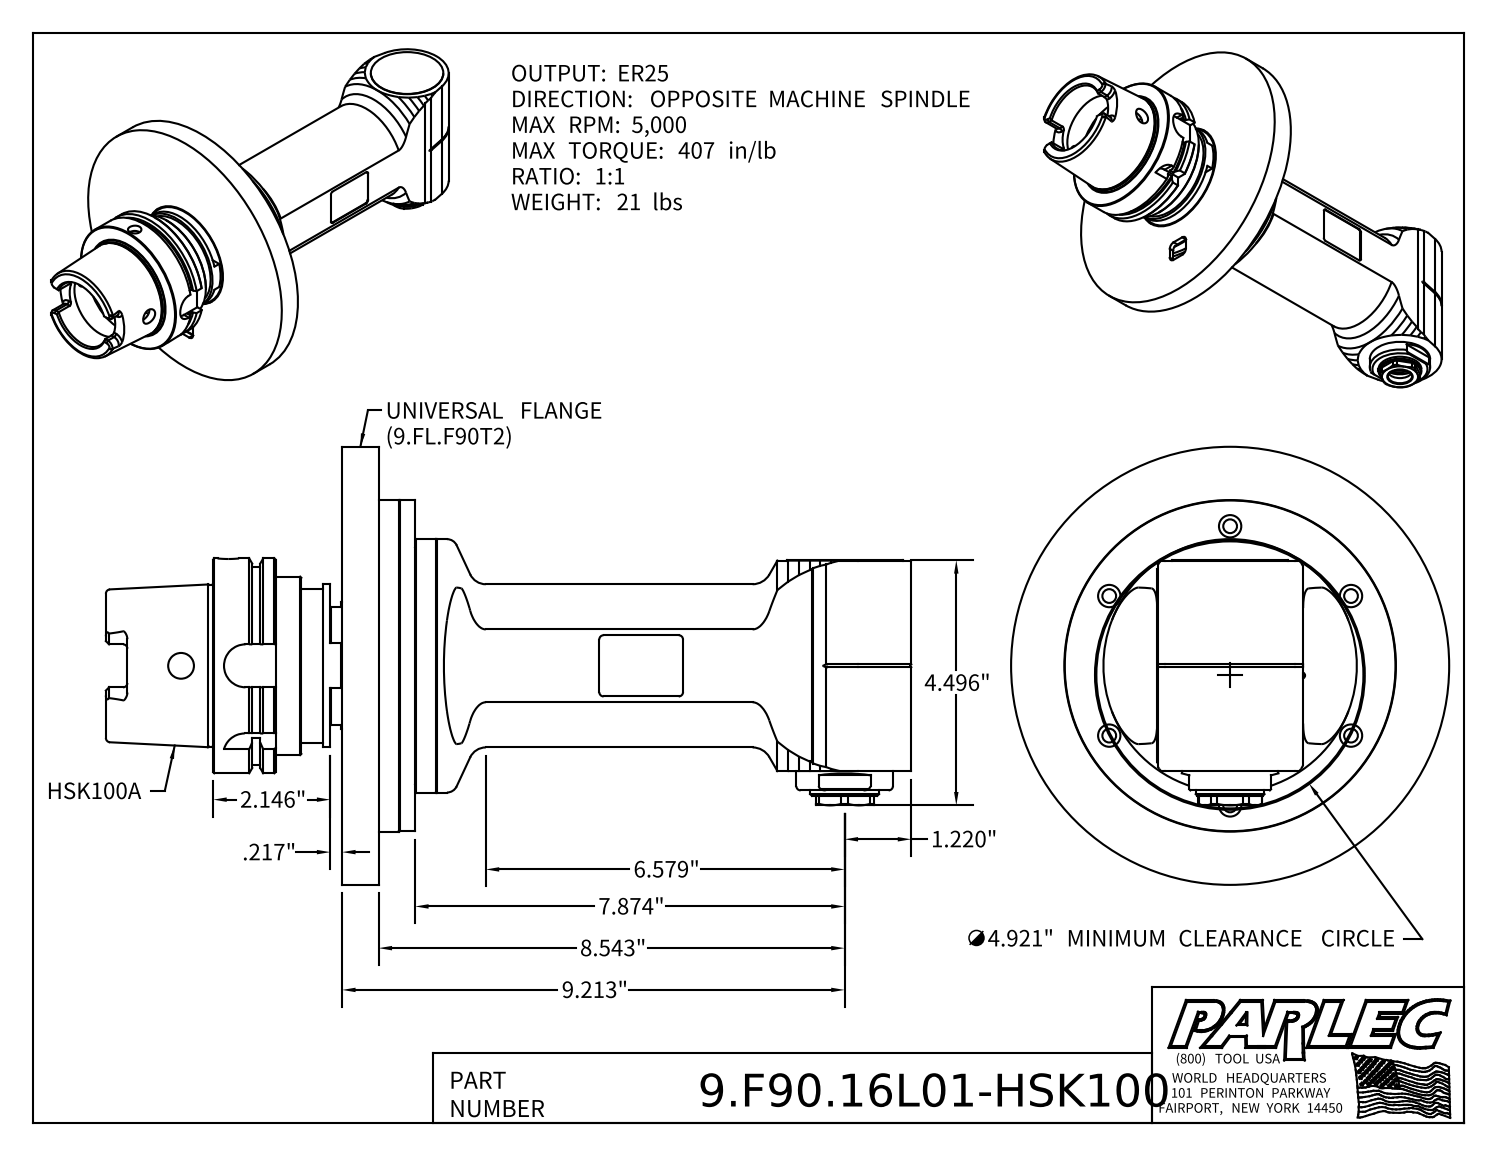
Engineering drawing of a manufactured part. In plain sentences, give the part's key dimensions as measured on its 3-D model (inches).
The part is named "9.F90.16L01-HSK100; 9_SK_51_2 (EVO, HSK100, MTC); 9_F90_16L01". Its 3-D file was written by "Autodesk Inventor 2022 (AUTOMOTIVE_DESIGN)". It is 4 solids with 429 faces: 186 planar, 121 cylindrical and 122 other. Overall it measures 14.764 by 8.031 by 8.031 inches. Its volume is 148 cubic inches and its surface area 448.8 square inches. Round holes: 10 of diameter 0.409, 6 of diameter 0.252, 1 of diameter 0.394, 1 of diameter 0.472, 1 of diameter 0.492, 1 of diameter 0.709, 1 of diameter 0.787, 1 of diameter 1.008, 1 of diameter 1.102, 1 of diameter 1.201, 1 of diameter 1.28, 1 of diameter 2.087. Round bosses or shafts: 4 of diameter 0.394, 4 of diameter 0.236, 2 of diameter 0.098, 1 of diameter 8.031, 1 of diameter 6.079, 1 of diameter 6.063, 1 of diameter 4.78, 1 of diameter 4.646. Partial cylindrical surfaces (rounded edges, fillets, slot ends): 19 of radius 0.079, 6 of radius 0.157, 4 of radius 0.192, 4 of radius 0.394, 2 of radius 0.016, 1 of radius 0.581, 1 of radius 1.22. The main face-to-face distances are 0.669, 1.339, 1.201, 0.531, 0.138, 0.886, 0.354, 2.677, 1.654, 1.555. The hole center spacings are 2.559, 4.432, 0.856, 1.813, 1.929, 2.728, 2.778, 3.581.
